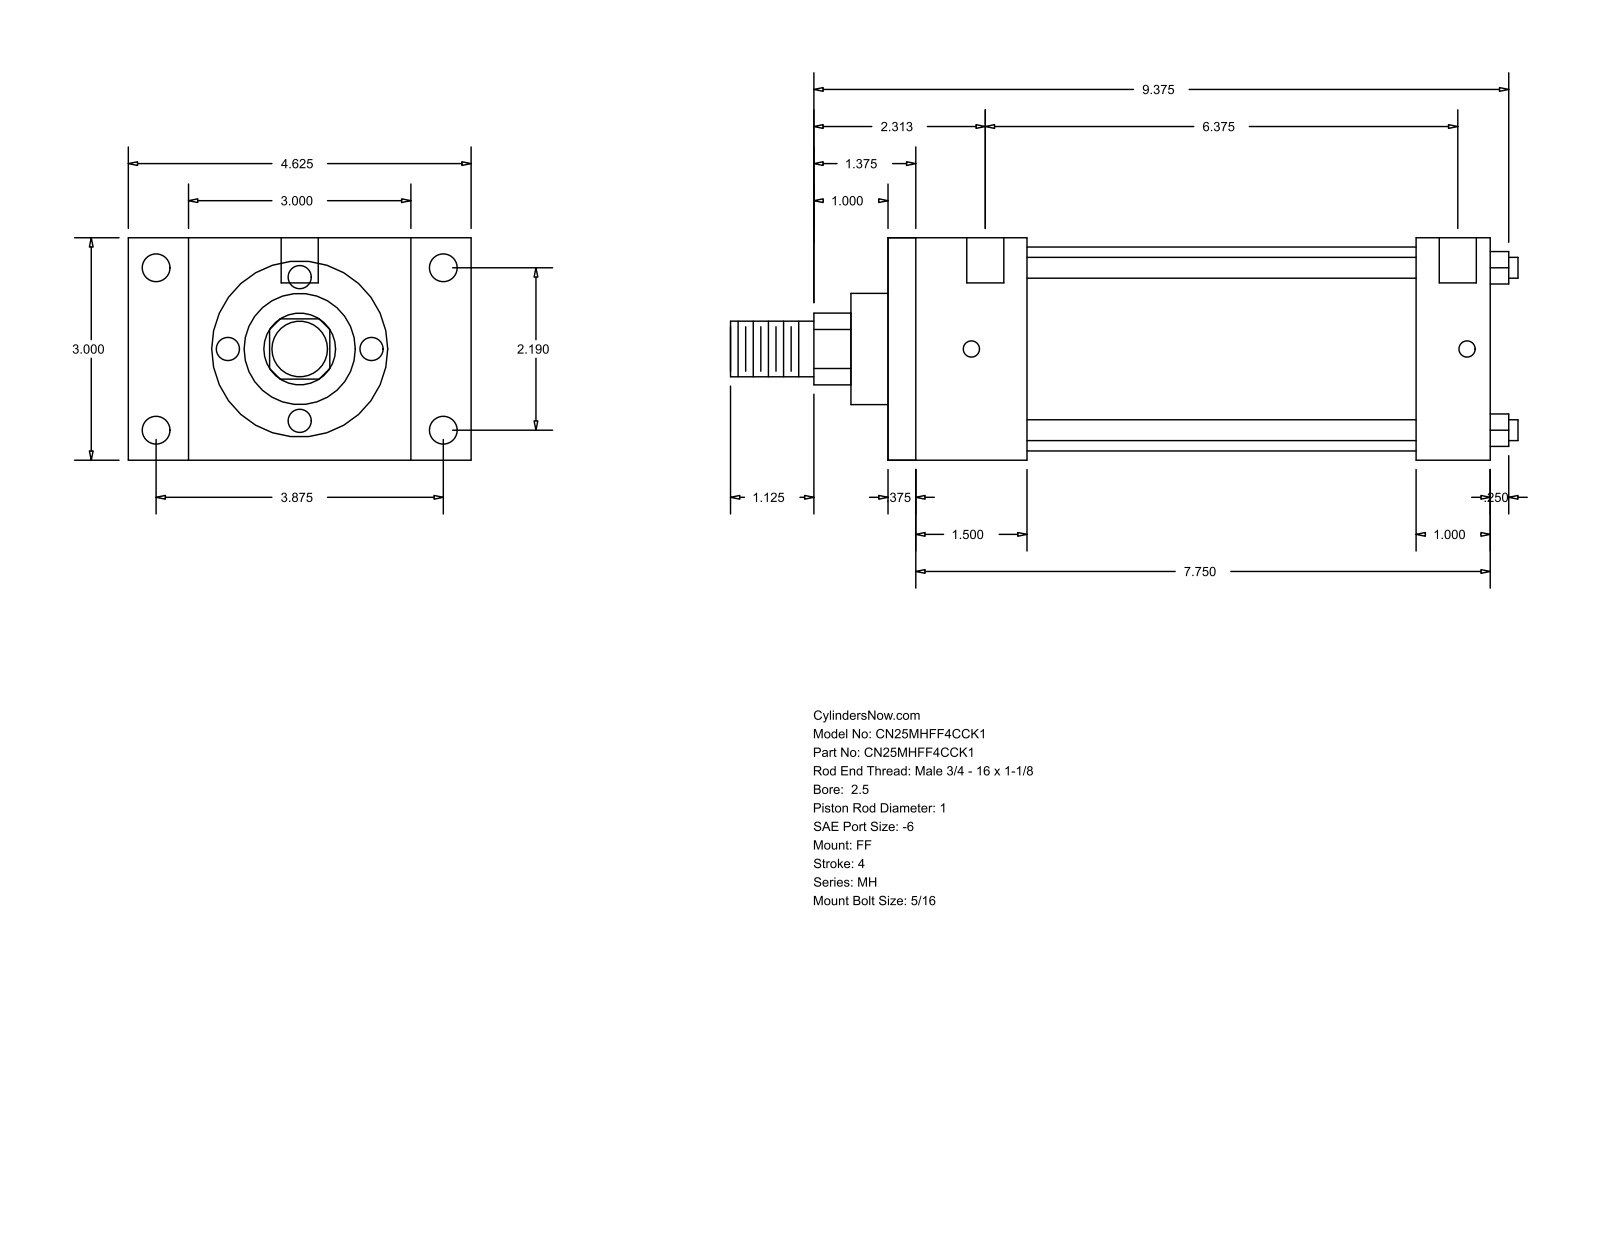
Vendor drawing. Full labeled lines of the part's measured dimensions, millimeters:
Part name (STEP PRODUCT): MH_FF__0250_1
STEP written by: GSSL Pune (CONFIG_CONTROL_DESIGN)
Units: millimetres
Bodies: 0 solids, 92 faces (64 planar, 28 cylindrical, 0 other)
Overall size (bounding box): 269.88 × 117.47 × 76.2
Round holes (diameter × count): ⌀5.56 ×4, ⌀9.53 ×4, ⌀12.7 ×2
Round bosses / shafts (diameter × count): ⌀7.14 ×4, ⌀69.85 ×1, ⌀38.1 ×1, ⌀25.4 ×1, ⌀19.05 ×1
Partial cylindrical surfaces — rounded edges, fillets, slot ends (radius × count): R12.29 ×1
Main face-to-face distances: 76.2, 206.38, 9.52, 196.86, 25.4, 47.63, 180.98, 38.11, 171.46, 133.35
Hole centre spacings: 55.62, 98.42, 113.05, 169.86, 3.18, 4.76, 161.92, 165.1
